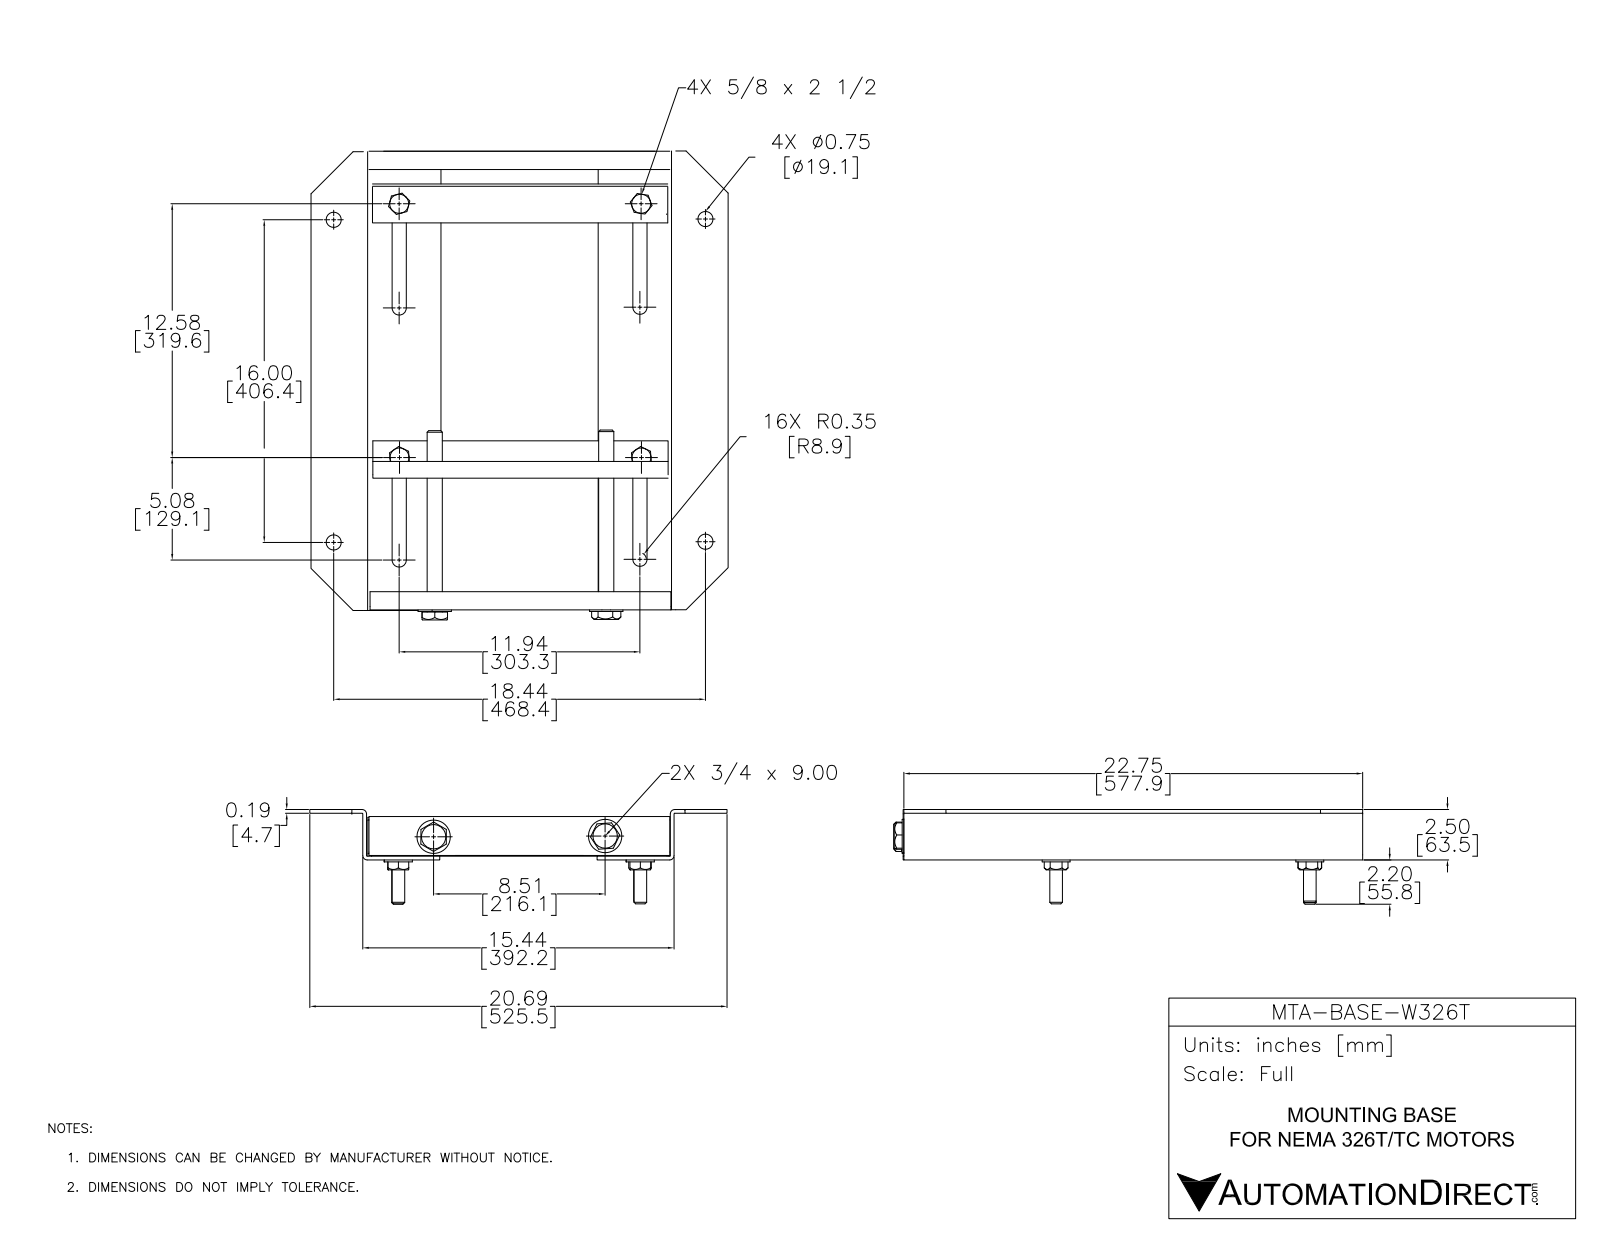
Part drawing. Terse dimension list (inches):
name: W326T
written by: SolidWorks 2017 (AUTOMOTIVE_DESIGN)
unit: in
bodies: 26 solids, 410 faces (224 planar, 110 cylindrical, 76 other)
size: 23.259 × 20.689 × 4.697
volume: 112.9 in³; area: 1 350 in²
holes: 8× ⌀0.75, 4× ⌀0.63, 4× ⌀0.65, 4× ⌀0.866, 3× ⌀0.625, 2× ⌀0.787, 1× ⌀0.625
bosses: 4× ⌀1.386, 2× ⌀1.654, 1× ⌀0.625
rounds: 11× R0.029, 8× R0.35, 6× R0.167, 4× R0.214, 1× R0.147
face distances: 0.185, 2.315, 0.138, 2.5, 2.13, 15.254, 1.791, 0.118, 22.608, 15.439
hole spacings: 0.036, 8.504, 12, 12.582, 16, 18.439, 3.278, 3.345
